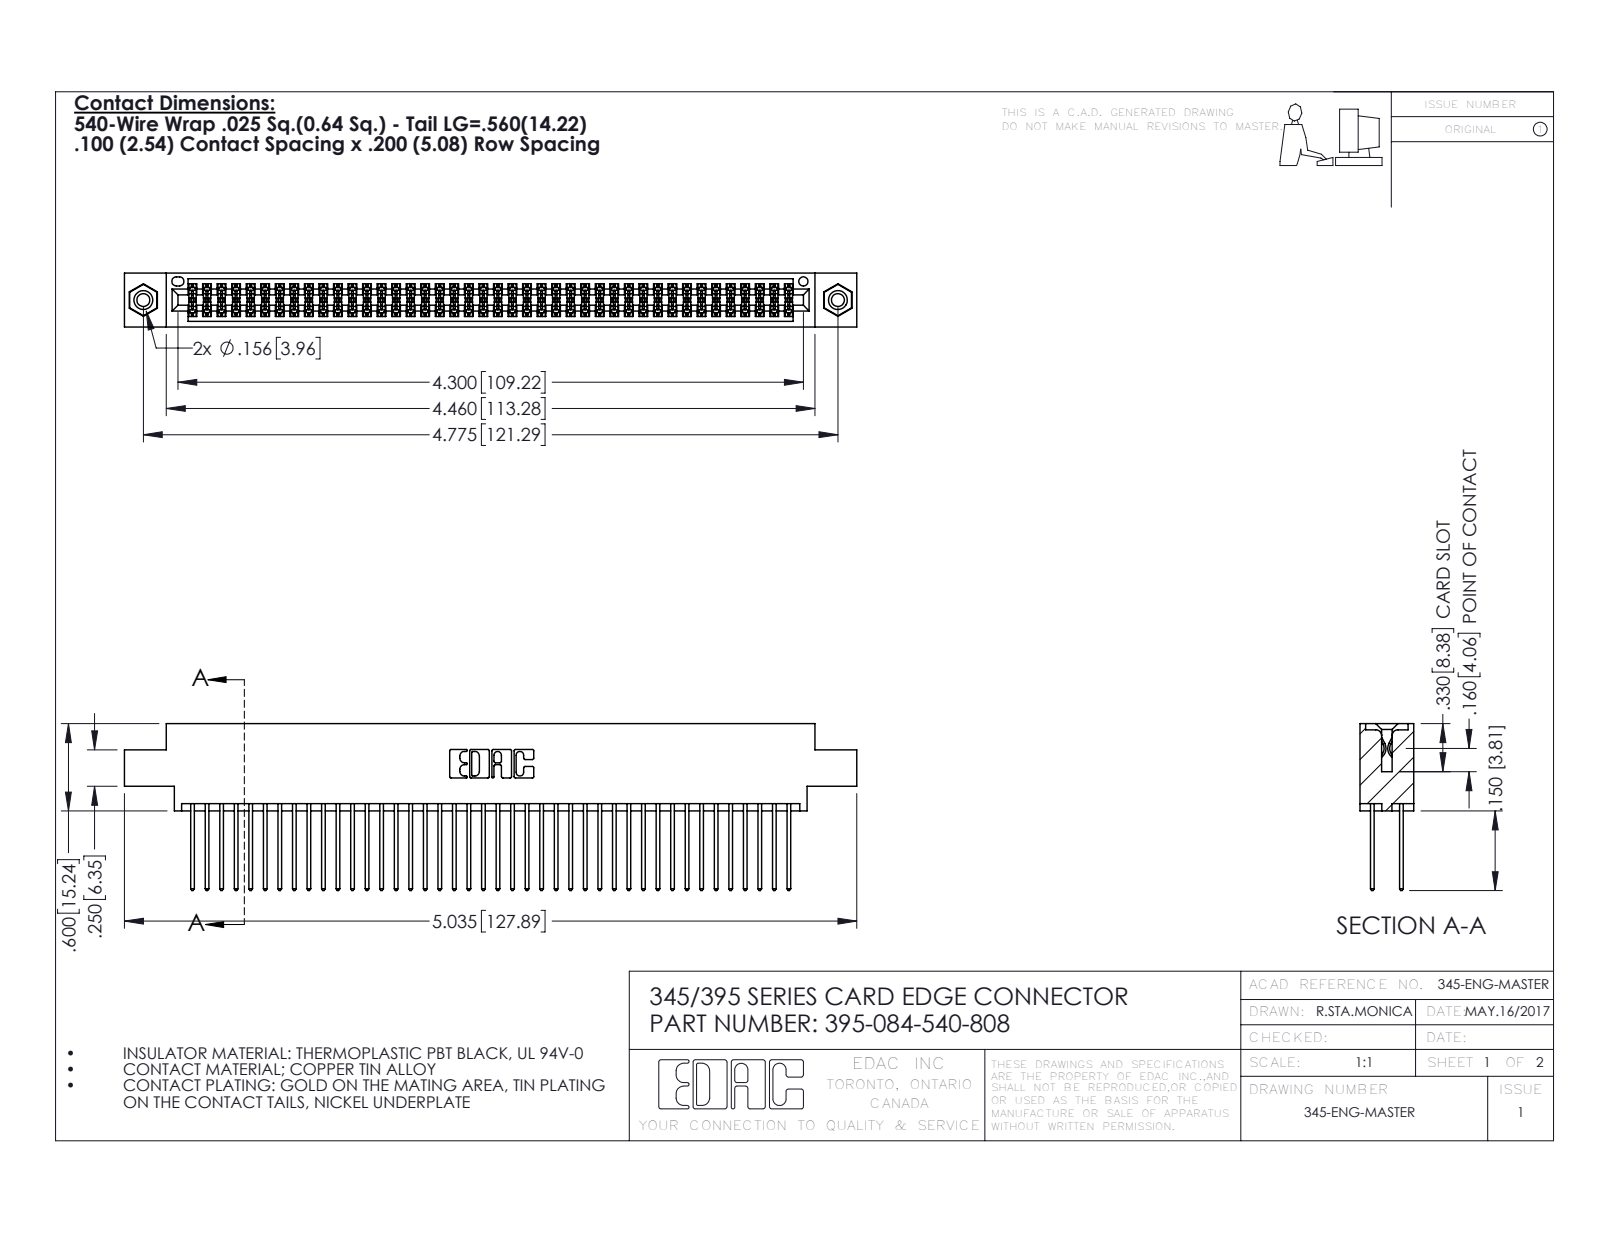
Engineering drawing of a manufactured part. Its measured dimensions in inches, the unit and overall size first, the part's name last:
Units: inches
Overall size (bounding box): 5.035 × 1.147 × 0.37
Round holes (diameter × count): ⌀0.089 ×2, ⌀0.125 ×2, ⌀0.156 ×2, ⌀0.064 ×1
Round bosses / shafts (diameter × count): ⌀0.155 ×2
Partial cylindrical surfaces — rounded edges, fillets, slot ends (radius × count): R0.006 ×126, R0.01 ×84, R0.01 ×22, R0.007 ×6, R0.031 ×6, R0.026 ×3, R0.014 ×2, R0.019 ×2
Main face-to-face distances: 0.072, 0.298, 0.2, 0.098, 0.272, 0.025, 0.37, 0.225, 0.175, 0.149
Hole centre spacings: 0.27, 4.539, 4.775
Volume: 0.77 in³ · Surface area: 31.45 in²
Bodies: 87 solids, 4390 faces (2888 planar, 1486 cylindrical, 16 other)
Part name (STEP PRODUCT): 345-250-001_345-250-003-102; 345 Part_0.170 Offset - 0.156 Dia-TI; 395-084-540-808; 345-292-001_345-293-140
STEP written by: SolidWorks 2016 (CONFIG_CONTROL_DESIGN)
